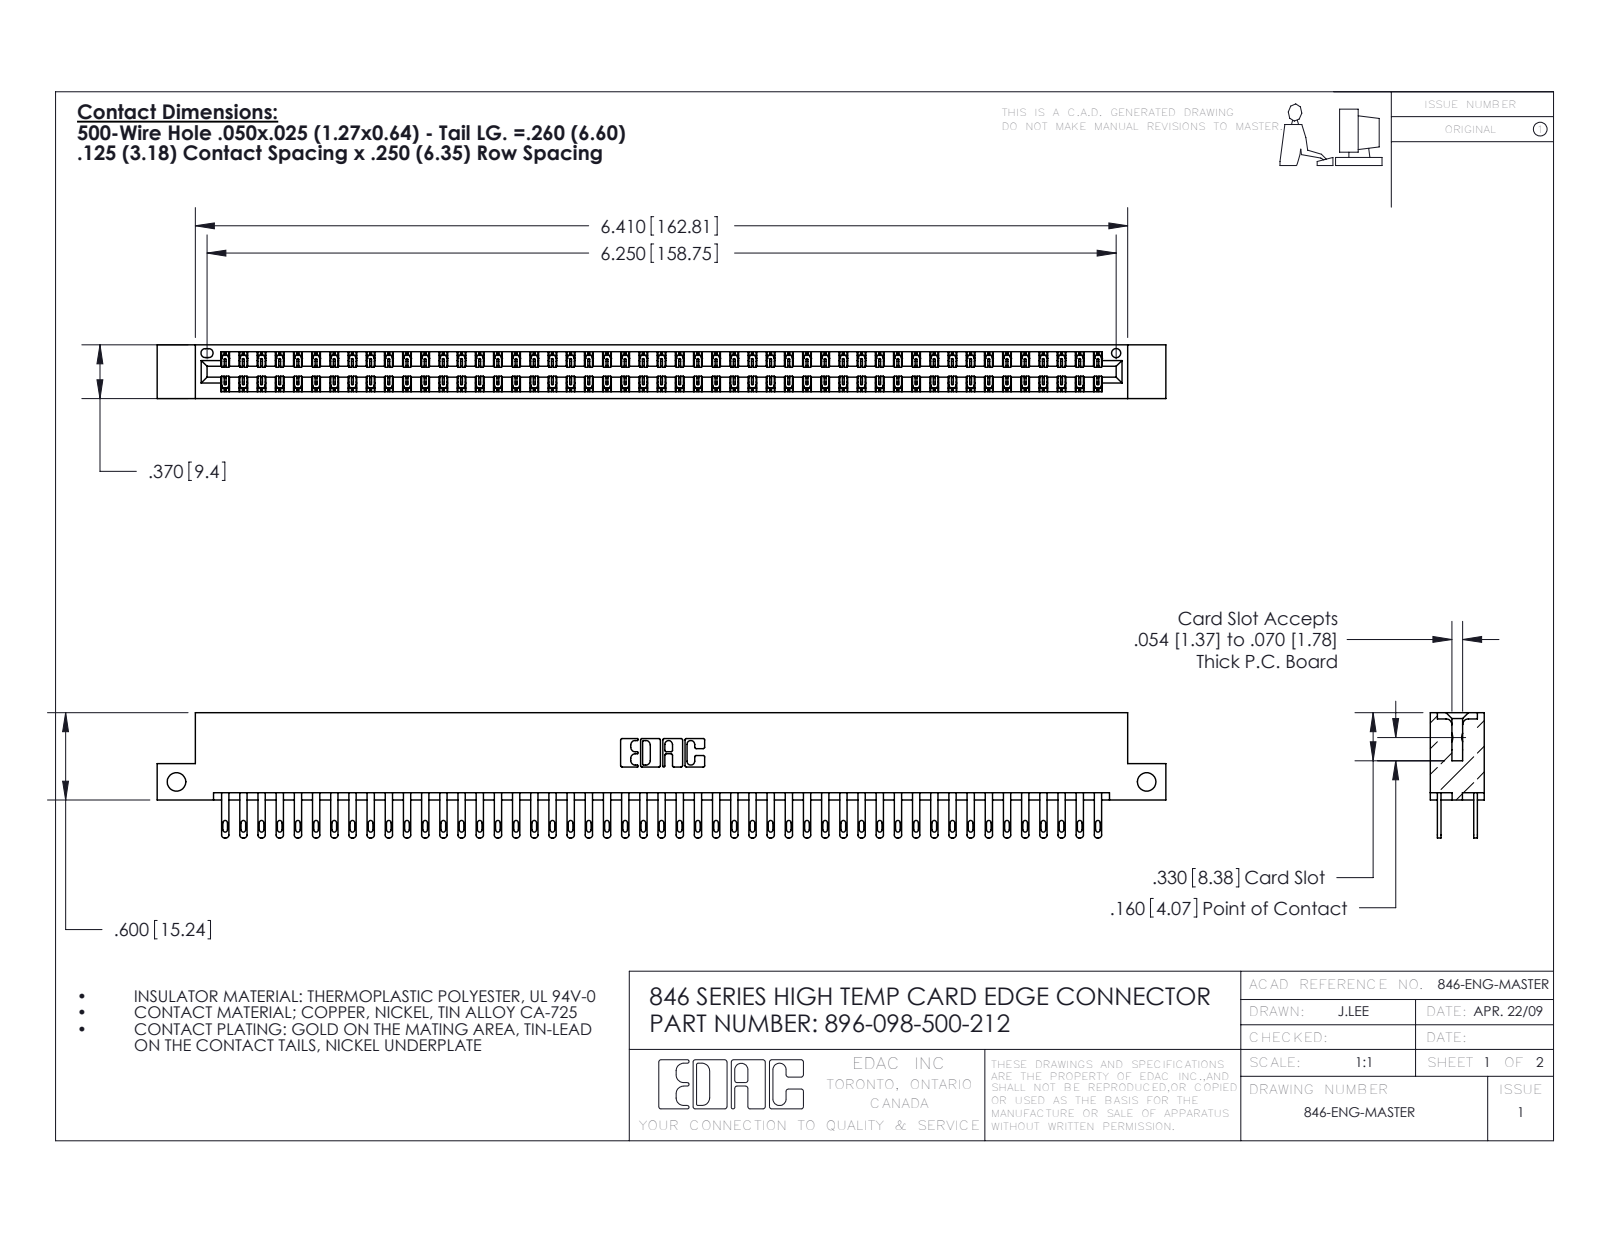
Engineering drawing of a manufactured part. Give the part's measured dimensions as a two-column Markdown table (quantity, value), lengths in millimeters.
| quantity | value |
| --- | --- |
| part name | 896-098-500-212; 846 Part_Flush Mounting Lugs - Side Mount; 345-292-001_345-293-100 |
| STEP written by | SolidWorks 2020 (CONFIG_CONTROL_DESIGN) |
| units | millimeters |
| bodies | 99 solids, 4826 faces (2918 planar, 1908 cylindrical, 0 other) |
| overall size | 176.1 × 21.8 × 9.4 |
| volume | 17 440 mm³ |
| surface area | 24 970 mm² |
| round holes (diameter × count) | 3.3 × 2, 1.6 × 1 |
| partial cylindrical surfaces (radius × count) | 0.2 × 147, 0.4 × 98, 0.5 × 98, 0.3 × 22, 0.2 × 6, 0.8 × 6, 0.7 × 3, 0.4 × 2 |
| main face-to-face distances | 1.2, 8.2, 6.4, 1.8, 7.6, 0.6, 9.4, 7, 3.8, 5.6 |
| hole center spacings | 169.4 |
